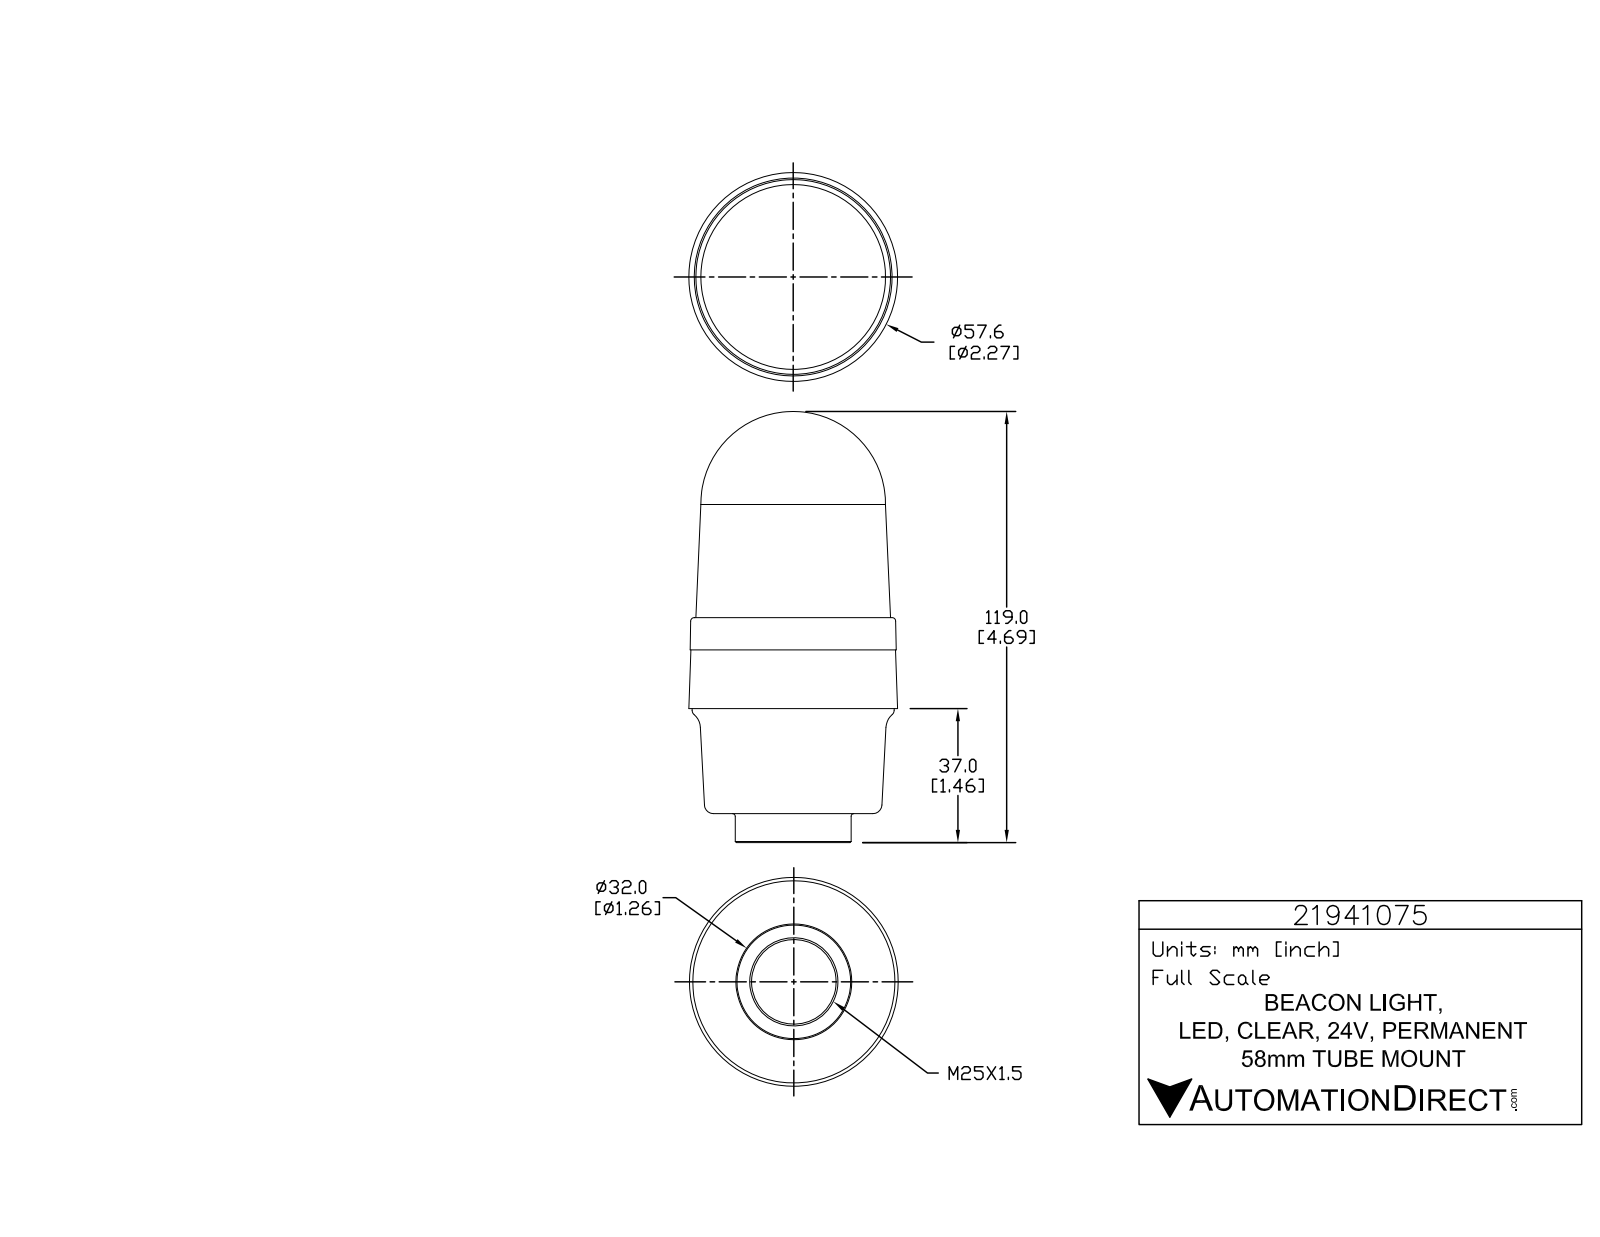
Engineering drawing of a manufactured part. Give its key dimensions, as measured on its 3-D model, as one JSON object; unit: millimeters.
{"part_name": "21941075", "step_written_by": "SolidWorks 2015 (AUTOMOTIVE_DESIGN)", "units": "millimeters", "bodies": {"solids": 1, "faces": 791, "planar": 525, "cylindrical": 168, "other": 98}, "overall_size": [119, 57.6, 57.6], "volume_mm3": 227600, "surface_area_mm2": 21970, "round_holes": [[1, 3], [23.4, 1]], "round_bosses_or_shafts": [[5.7, 3], [1.4, 3], [55.8, 1], [32, 1]], "partial_cylinders_radius": [[0.2, 6], [0.2, 6], [0.2, 6], [3.3, 6], [0.1, 3], [0.1, 3], [0.2, 3], [0.2, 3]], "face_to_face_distances": [8, 29, 37, 25.1, 54.1, 62.1, 8.9, 16.2, 45.2, 53.2]}
